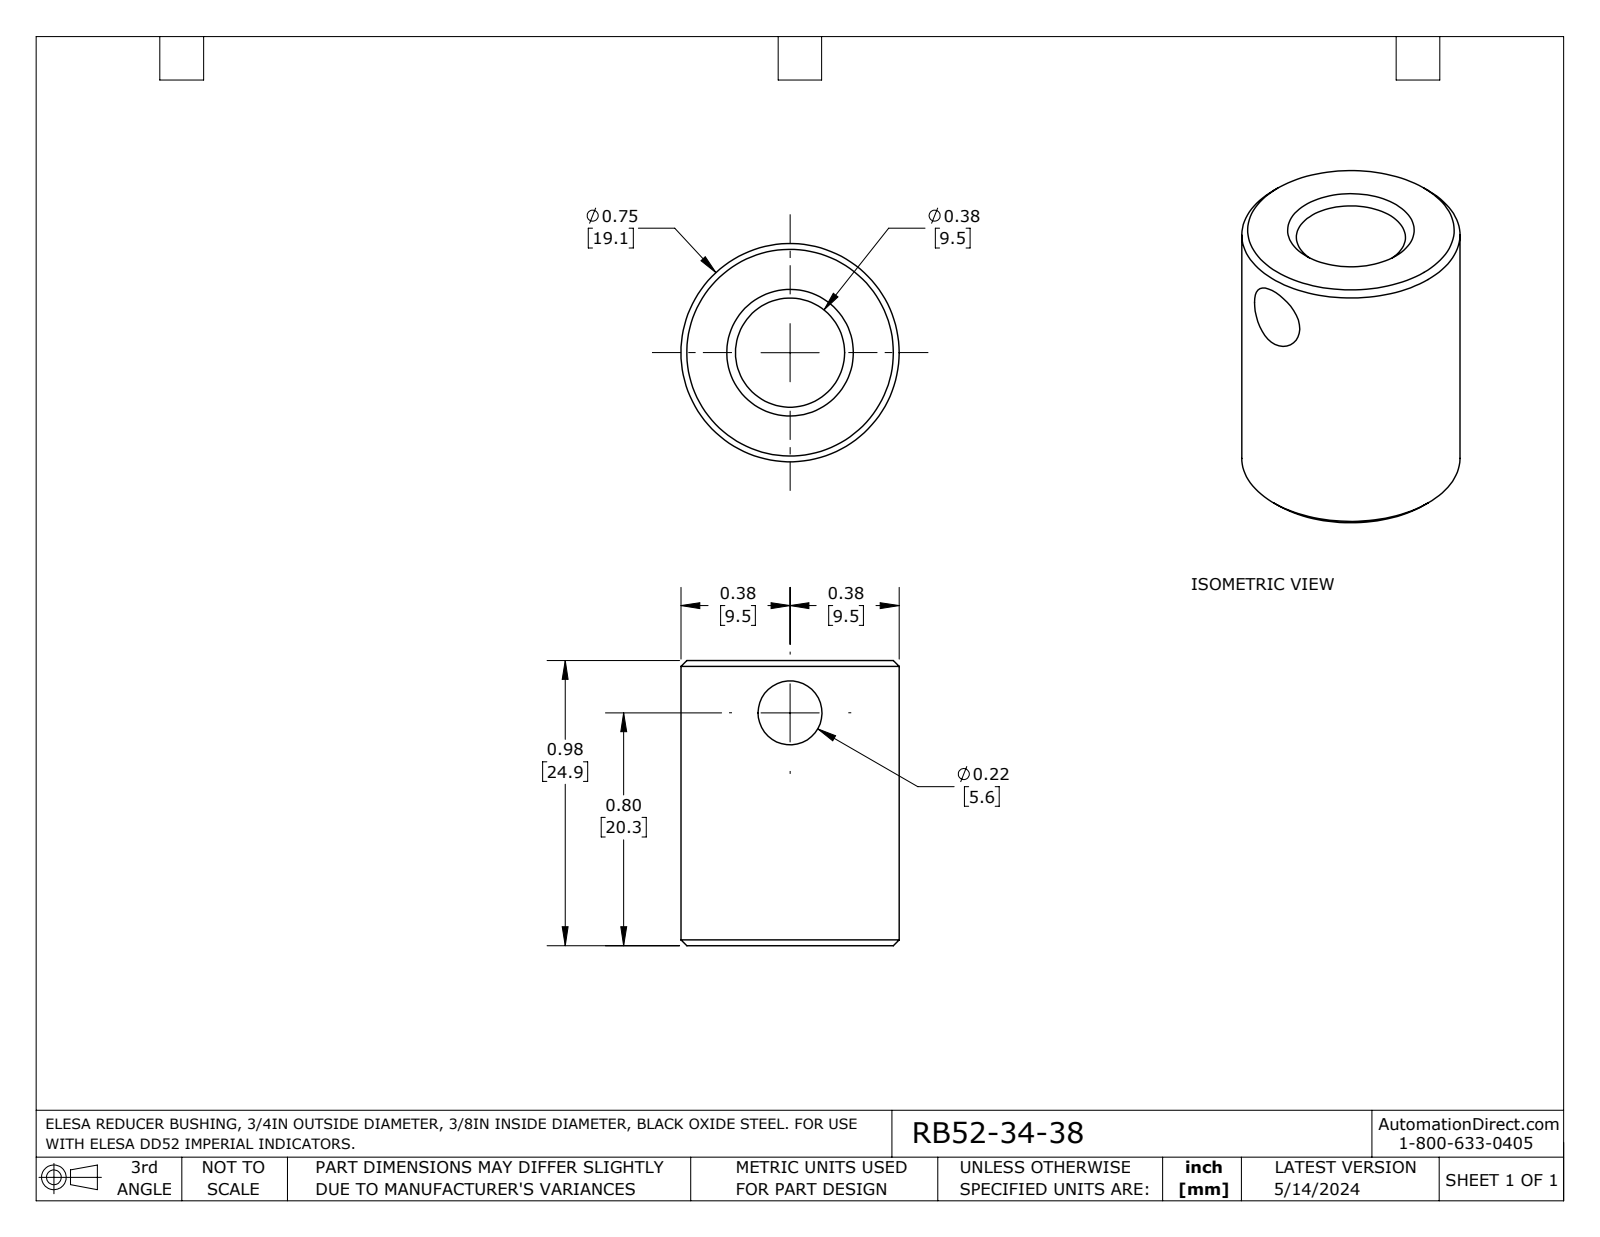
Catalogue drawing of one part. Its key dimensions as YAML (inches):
part_name: "RB52 3_4-3_8"
step_written_by: "SolidWorks 2023 (AUTOMOTIVE_DESIGN)"
units: inches
bodies: {solids: 1, faces: 9, planar: 2, cylindrical: 3, other: 4}
overall_size: [0.98, 0.75, 0.75]
volume: 0.315
surface_area: 4.088
round_holes:
  - {diameter: 0.22, count: 1}
  - {diameter: 0.375, count: 1}
round_bosses_or_shafts:
  - {diameter: 0.75, count: 1}
face_to_face_distances: [0.98]
